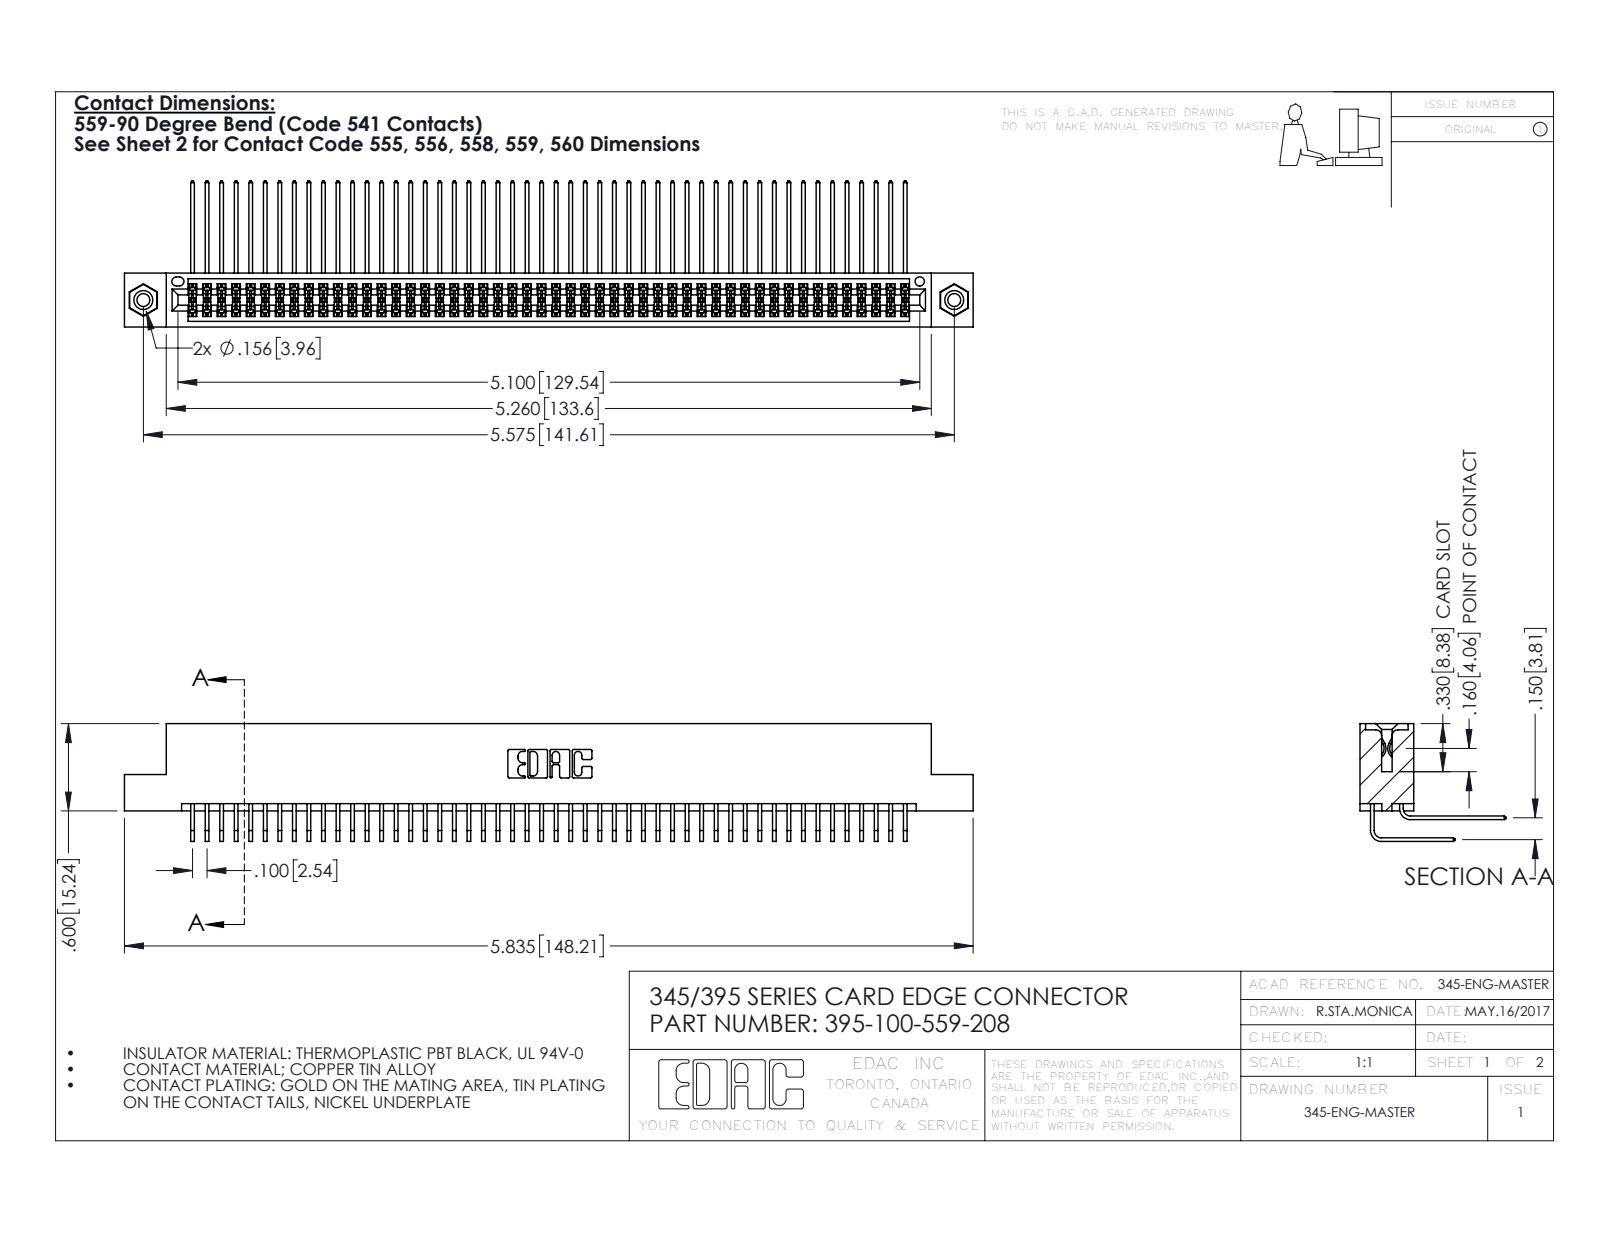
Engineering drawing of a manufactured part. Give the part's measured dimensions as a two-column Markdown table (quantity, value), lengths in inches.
| quantity | value |
| --- | --- |
| part name | 345-250-001_345-250-003-102; 345 Part_Flush Mounting Lugs - 0.156 Dia-TI; 345-292-001_558 559 Tail - 1; 345-292-001_559 Tail - 2 (+1 more) |
| STEP written by | SolidWorks 2016 (CONFIG_CONTROL_DESIGN) |
| units | inches |
| bodies | 103 solids, 5386 faces (3612 planar, 1758 cylindrical, 16 other) |
| overall size | 5.835 × 1.005 × 0.809 |
| volume | 0.918 in³ |
| surface area | 38.93 in² |
| round holes (diameter × count) | 0.089 × 2, 0.125 × 2, 0.156 × 2, 0.064 × 1 |
| round bosses / shafts (diameter × count) | 0.155 × 2 |
| partial cylindrical surfaces (radius × count) | 0.006 × 151, 0.01 × 22, 0.007 × 6, 0.031 × 6, 0.026 × 3, 0.014 × 2, 0.019 × 2, 0.022 × 2 |
| main face-to-face distances | 0.072, 0.298, 0.2, 0.37, 0.098, 0.272, 0.025, 0.225, 0.175, 0.15 |
| hole center spacings | 0.27, 5.339, 5.575 |
